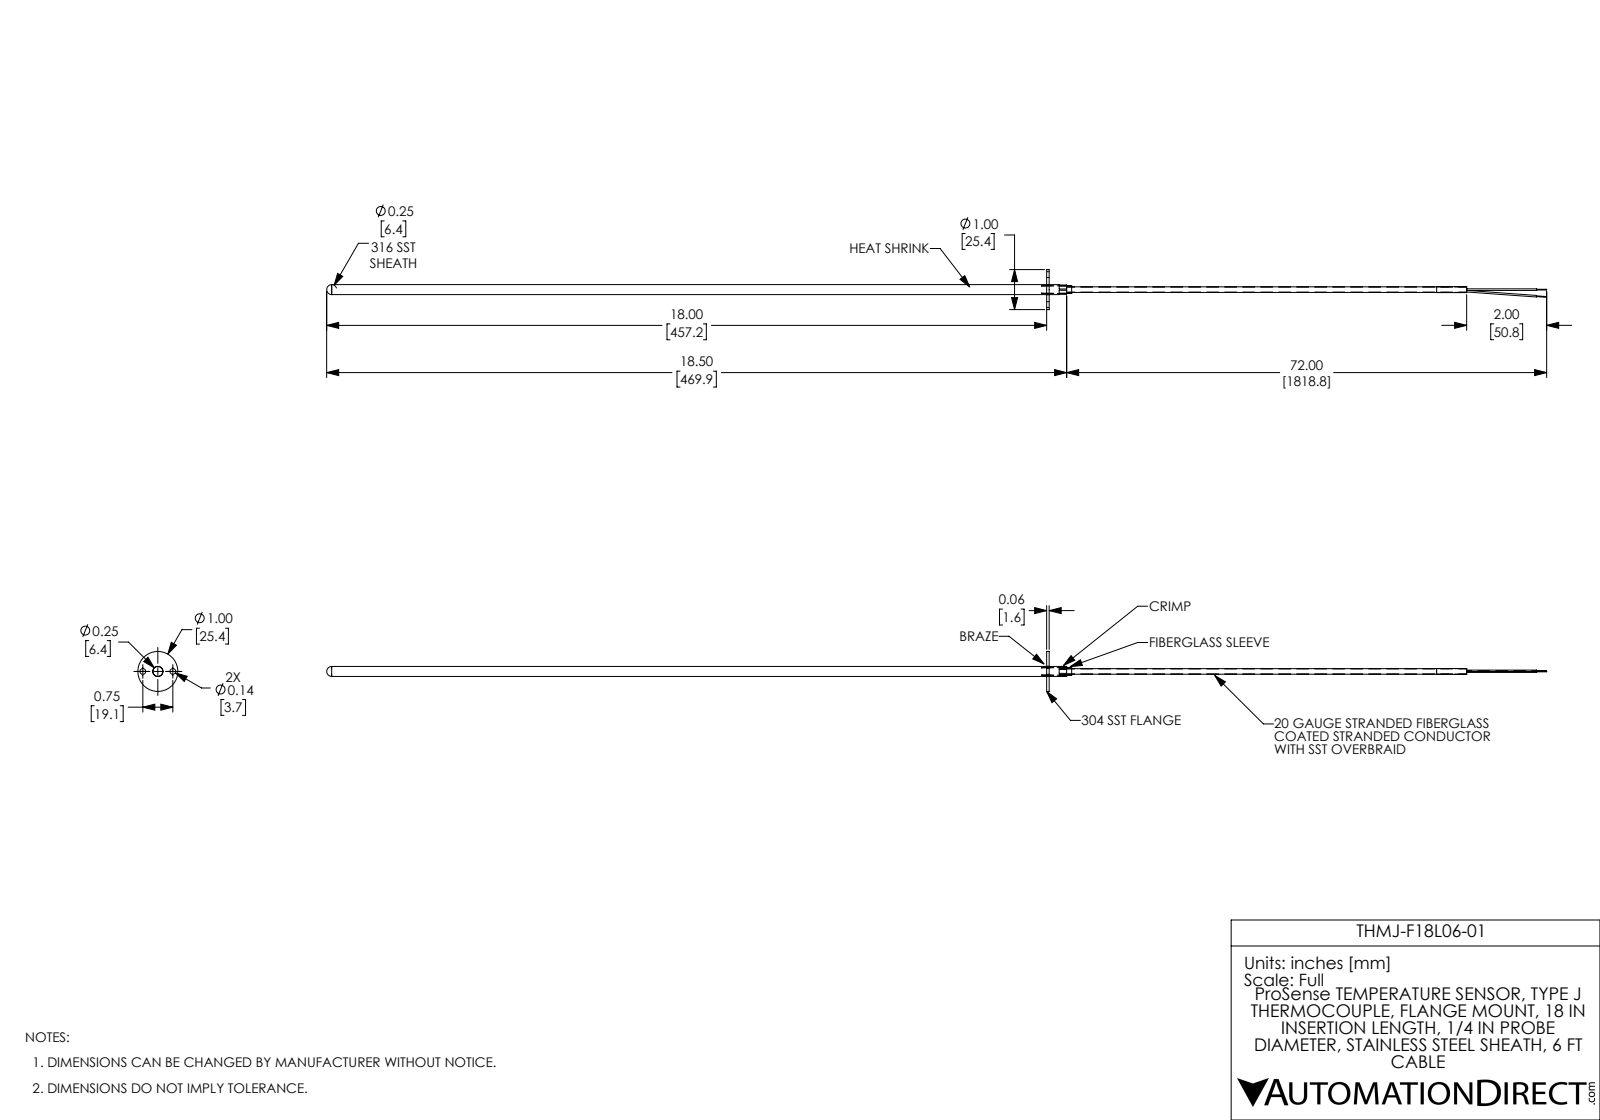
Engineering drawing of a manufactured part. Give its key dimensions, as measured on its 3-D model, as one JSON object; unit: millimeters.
{"part_name": "THMJ-F18L06-01", "step_written_by": "SolidWorks 2017 (AUTOMOTIVE_DESIGN)", "units": "millimeters", "bodies": {"solids": 7, "faces": 65, "planar": 30, "cylindrical": 32, "other": 3}, "overall_size": [774.7, 25.4, 25.4], "volume_mm3": 18370, "surface_area_mm2": 20440, "round_holes": [[3.7, 3], [3.5, 1], [4.8, 1], [6.5, 1]], "round_bosses_or_shafts": [[25.4, 1], [6.4, 1], [4.8, 1], [4.8, 1], [3.8, 1], [3.6, 1], [3.4, 1], [1, 1]], "face_to_face_distances": [1.6, 12.7, 11.1, 5.9, 19.1, 3.2, 4.8, 15.9, 15.9, 14.3], "hole_center_spacings": [9.5, 9.5, 19.1]}
